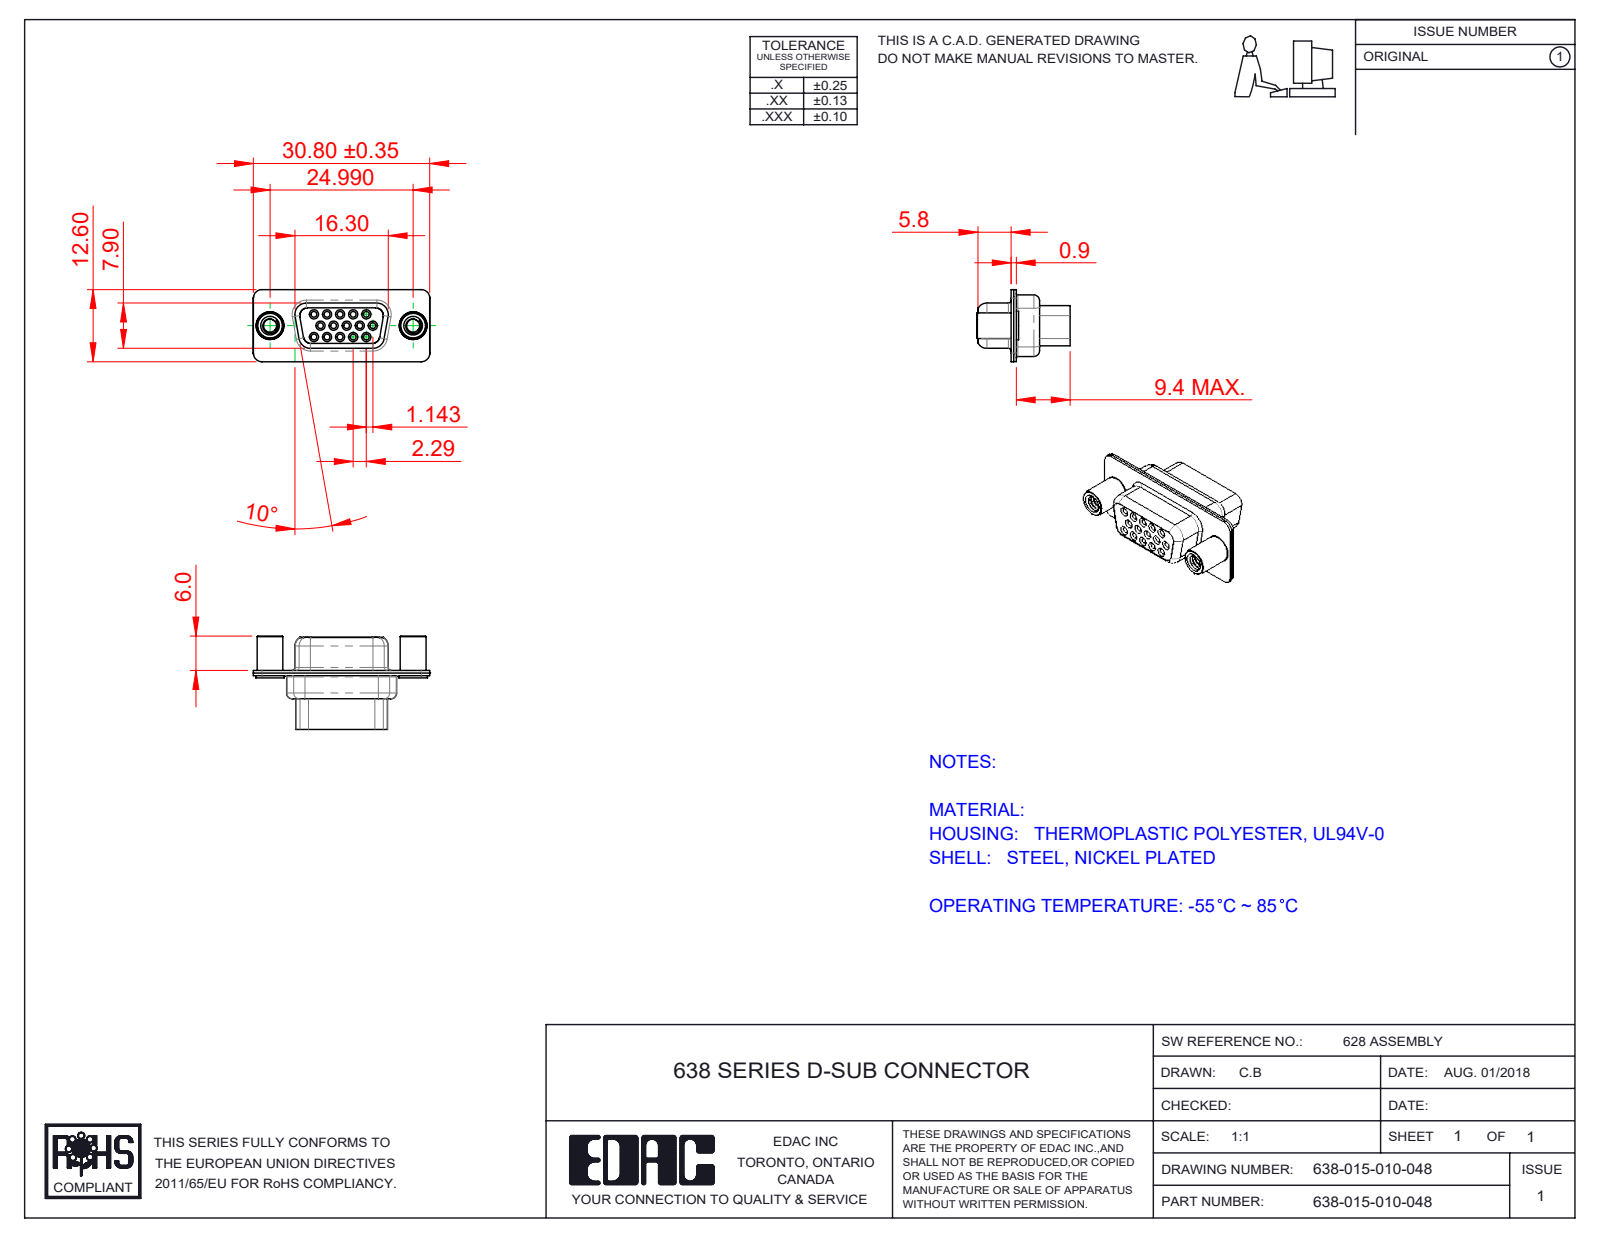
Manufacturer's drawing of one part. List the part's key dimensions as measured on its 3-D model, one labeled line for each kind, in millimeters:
Part name (STEP PRODUCT): 638 Housing_15 Contacts HP; 638 4-40 Threaded Standoff; 638 Shell Front_15 Contacts; 638 Shell Rear_15 Contacts (+1 more)
STEP written by: SolidWorks 2020 (CONFIG_CONTROL_DESIGN)
Units: millimetres
Bodies: 5 solids, 508 faces (114 planar, 285 cylindrical, 109 other)
Overall size (bounding box): 30.81 × 16.3 × 12.6
Volume: 1 774 mm³ · Surface area: 4 743 mm²
Round holes (diameter × count): ⌀1 ×15, ⌀1.7 ×15, ⌀1.8 ×15, ⌀2 ×15, ⌀2.26 ×2, ⌀4 ×2, ⌀4.05 ×2, ⌀4.85 ×2
Round bosses / shafts (diameter × count): ⌀5 ×2, ⌀4.95 ×2, ⌀4.8 ×2, ⌀4.5 ×2
Partial cylindrical surfaces — rounded edges, fillets, slot ends (radius × count): R1.5 ×20, R2 ×12, R1.55 ×8, R1.35 ×5, R0.25 ×4, R0.5 ×4, R0.55 ×4, R0.7 ×4
Main face-to-face distances: 0.45, 0.9, 0.4, 1.43, 8.88, 6.6, 7, 0.85, 9.4, 6.2
Hole centre spacings: 3.96, 2.28, 4.57, 2.29, 6.05, 6.86, 7.92, 6.04
